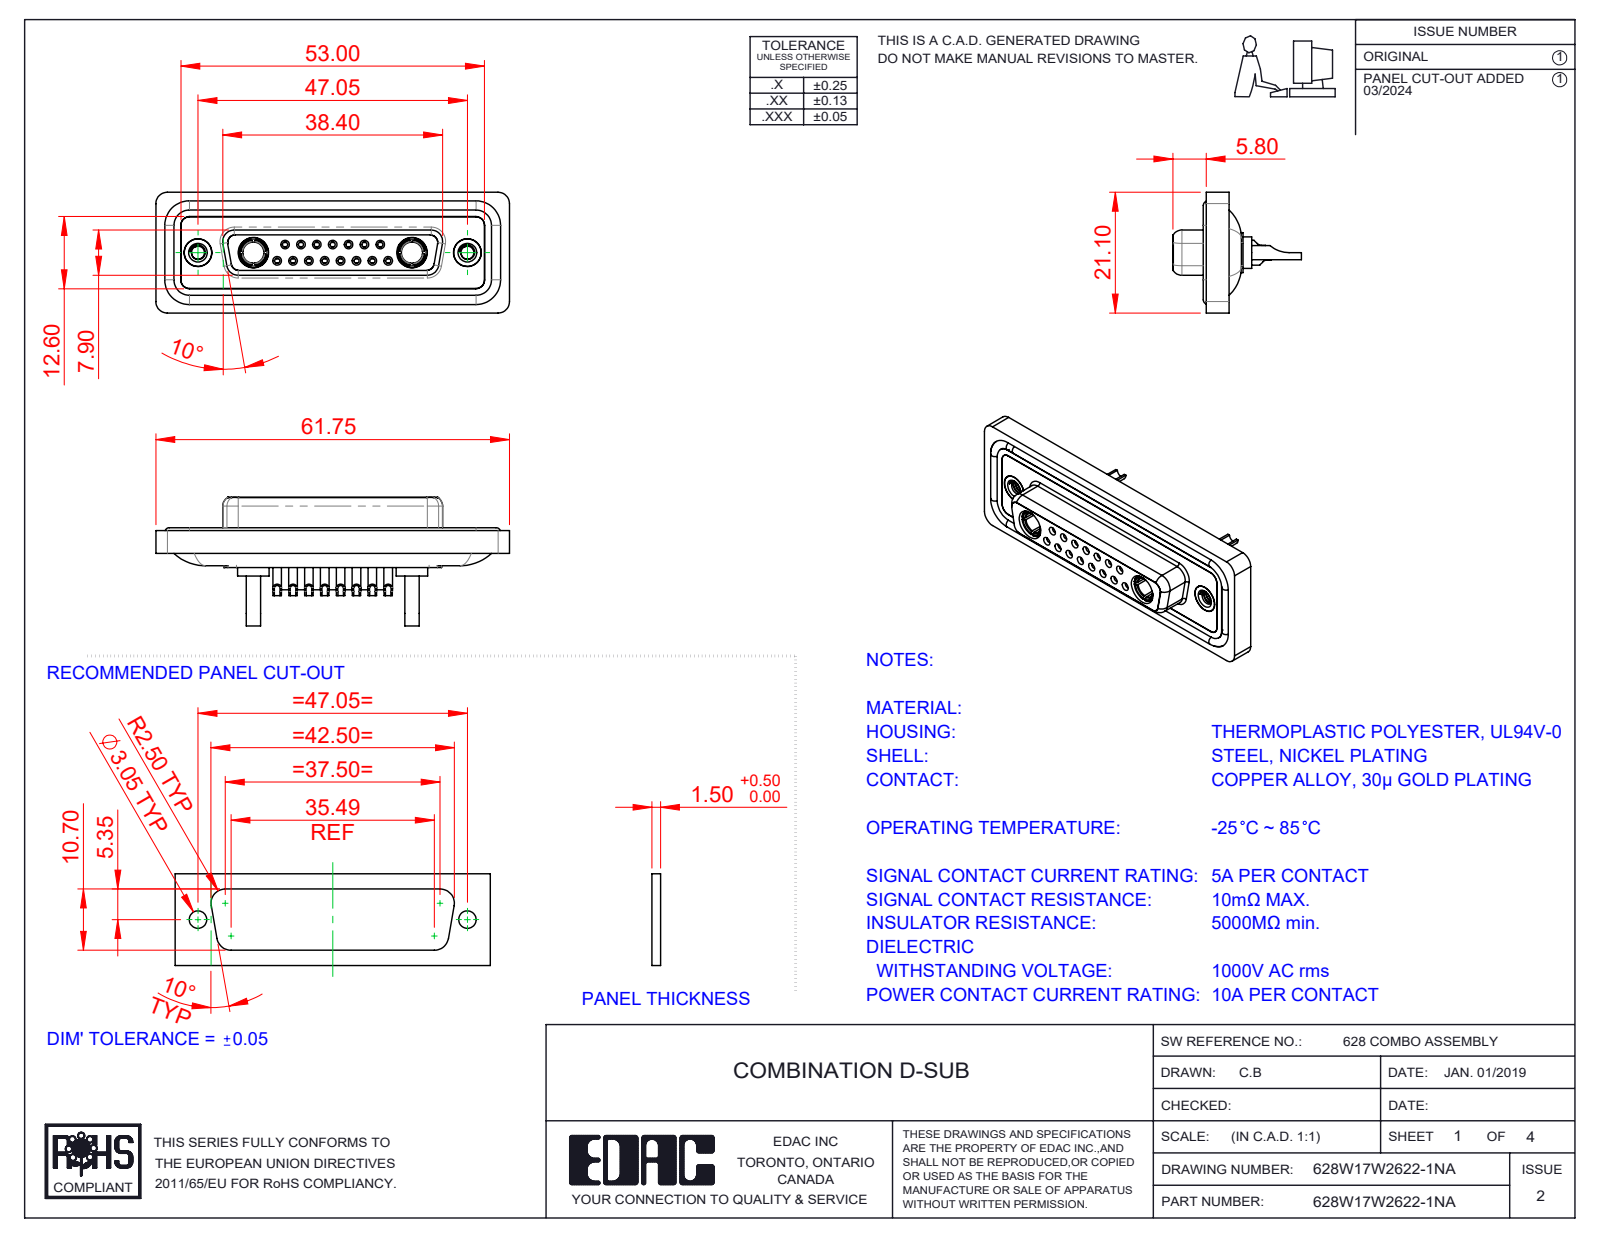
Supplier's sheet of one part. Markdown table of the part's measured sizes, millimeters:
| quantity | value |
| --- | --- |
| part name | 628Combo Waterproof Housing_25 Contacts; 628Combo Threaded Rivet_A; 628Combo Housing_17W2; 628Combo Shell Rear_25 Contacts (+5 more) |
| STEP written by | SolidWorks 2023 (CONFIG_CONTROL_DESIGN) |
| units | millimeters |
| bodies | 26 solids, 1367 faces (422 planar, 557 cylindrical, 388 other) |
| overall size | 61.75 × 22.45 × 21.1 |
| volume | 8 351 mm³ |
| surface area | 14 108 mm² |
| round holes (diameter × count) | 0.9 × 15, 1 × 15, 1.1 × 15, 1.5 × 15, 2 × 15, 1.6 × 8, 1.7 × 7, 4.85 × 4, 1.7 × 2, 2.26 × 2, 3.7 × 2, 4 × 2 |
| round bosses / shafts (diameter × count) | 2.2 × 15, 1.6 × 11, 5.5 × 2, 5.2 × 2, 4.96 × 2, 4.95 × 2, 4.8 × 2, 4.75 × 2 |
| partial cylindrical surfaces (radius × count) | 1.5 × 22, 2 × 18, 1.35 × 8, 1.6 × 8, 1 × 6, 0.25 × 4, 0.5 × 4, 0.6 × 4 |
| main face-to-face distances | 0.4, 1.8, 7.45, 5.65, 6.6, 0.5, 7.05, 1.6, 2.9, 1.1 |
| hole center spacings | 3.16, 2.77, 8.31, 5.54, 5.03, 5.04, 7.49, 11.08 |
